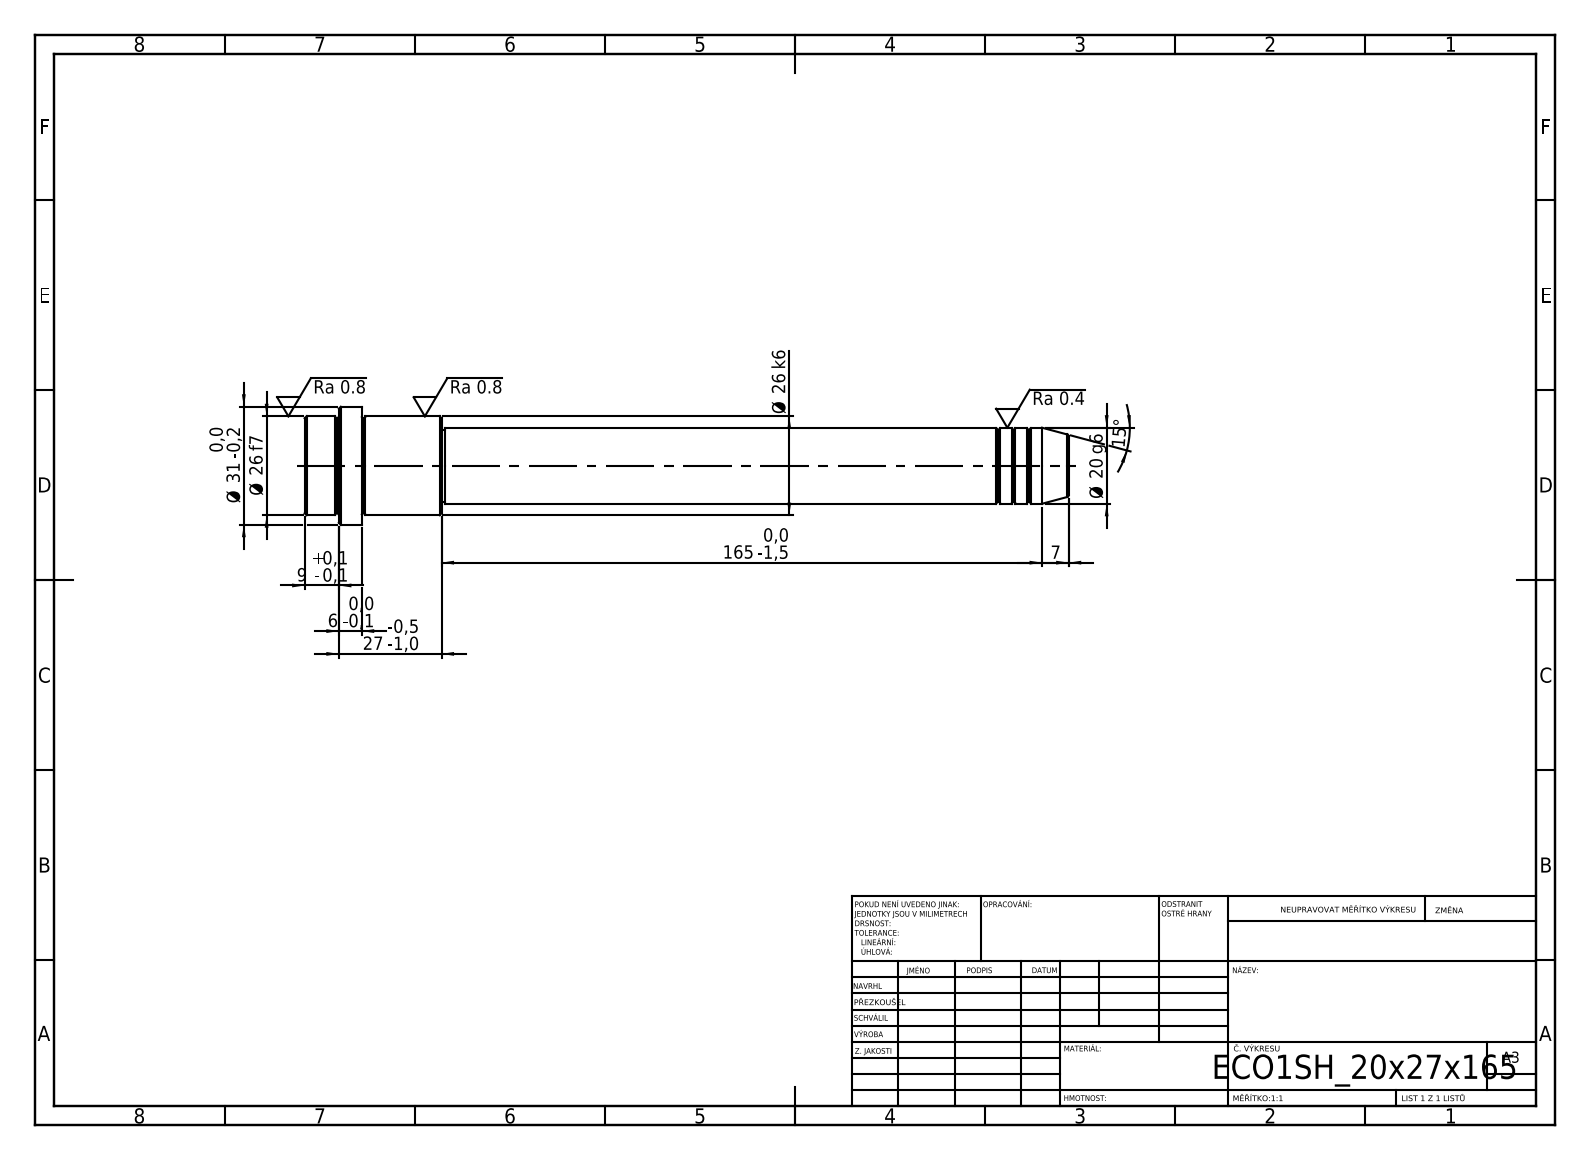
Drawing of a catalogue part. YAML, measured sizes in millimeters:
step_written_by: "SolidWorks 2019 (CONFIG_CONTROL_DESIGN)"
units: millimeters
bodies: {solids: 1, faces: 52, planar: 6, cylindrical: 16, other: 30}
overall_size: [201, 31, 31]
volume: 71706
surface_area: 14938
round_bosses_or_shafts:
  - {diameter: 31, count: 1}
  - {diameter: 26, count: 1}
  - {diameter: 20, count: 1}
  - {diameter: 19, count: 1}
face_to_face_distances: [15, 21, 36, 165, 186, 201, 192, 27, 6, 9]
